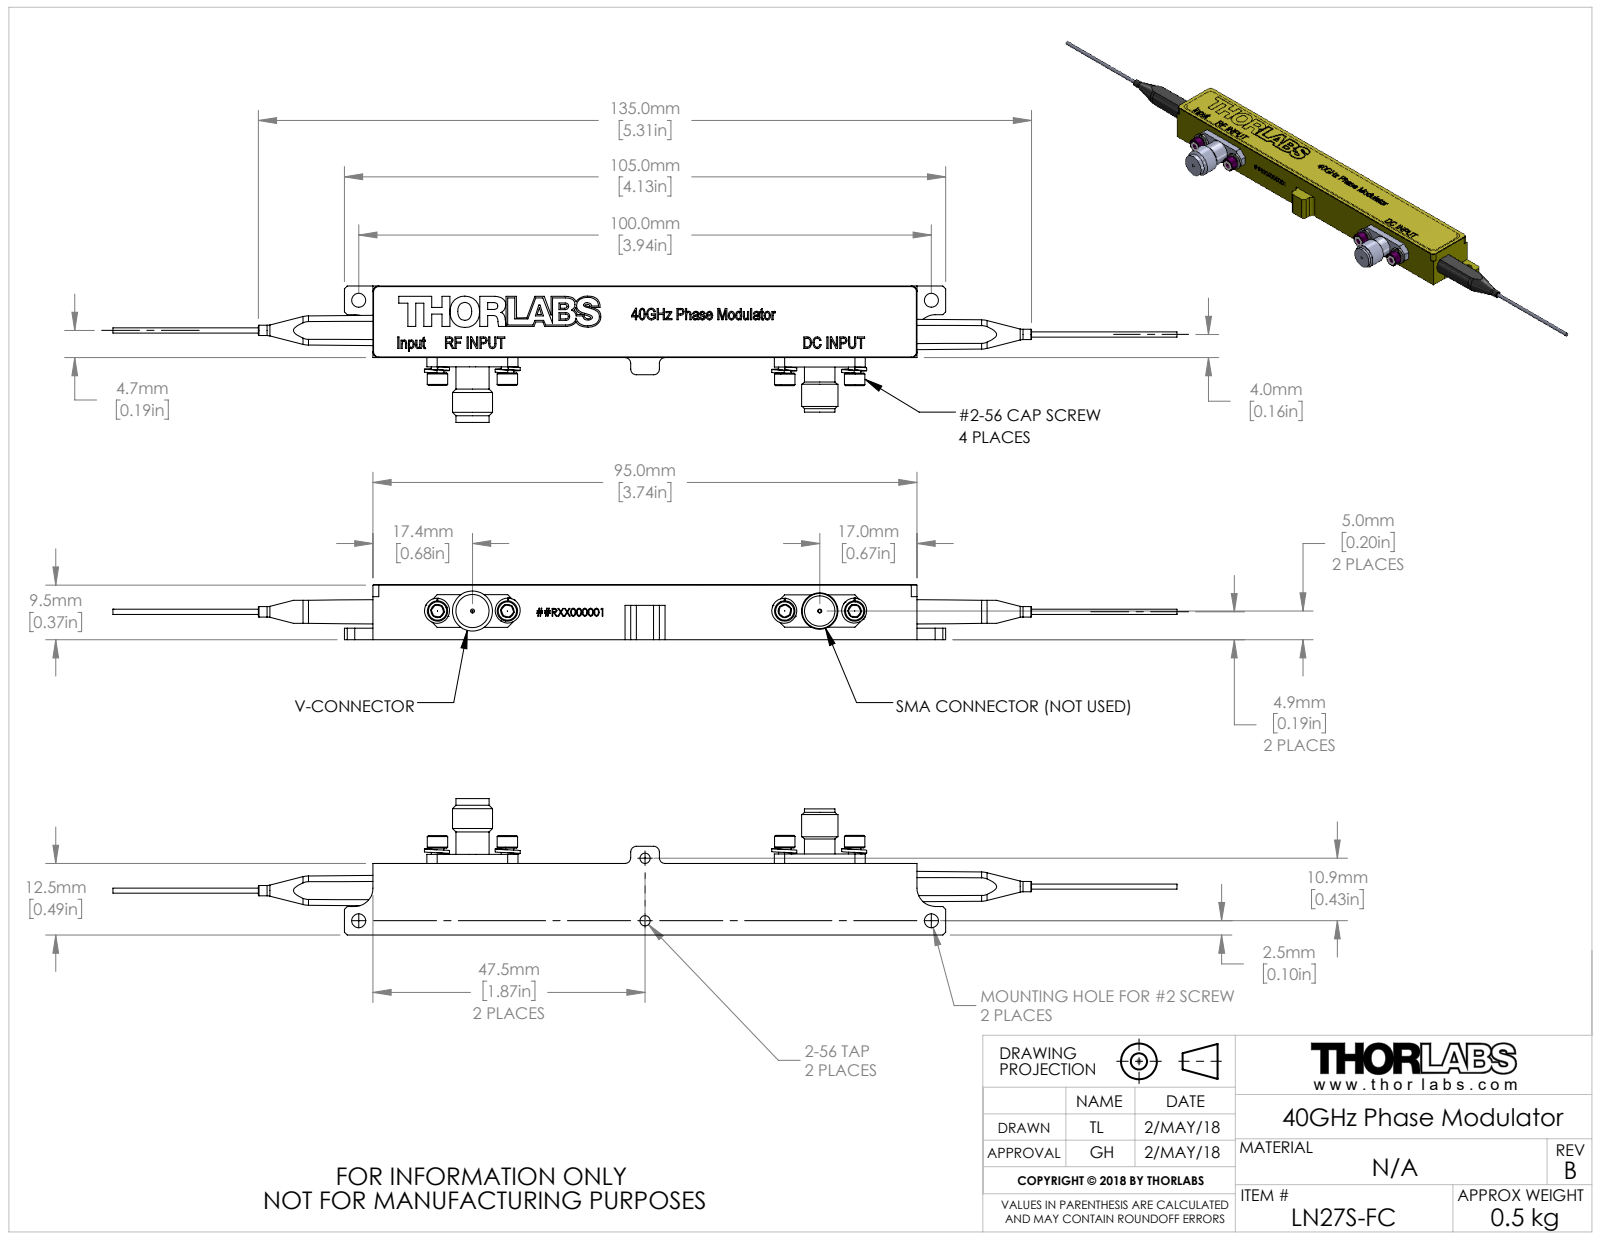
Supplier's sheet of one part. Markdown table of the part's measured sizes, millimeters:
| quantity | value |
| --- | --- |
| part name | 20857-E0W |
| STEP written by | SolidWorks 2016 (CONFIG_CONTROL_DESIGN) |
| units | millimeters |
| bodies | 0 solids, 583 faces (350 planar, 62 cylindrical, 171 other) |
| overall size | 185.8 × 23.81 × 9.63 |
| round holes (diameter × count) | 0.7 × 2, 1.78 × 2, 2.44 × 2 |
| round bosses / shafts (diameter × count) | 3.56 × 4, 2.18 × 4, 1.8 × 2, 0.9 × 2, 7 × 1, 6.35 × 1, 5.8 × 1, 5.31 × 1 |
| partial cylindrical surfaces (radius × count) | 1 × 8, 0.9 × 4, 3.18 × 2 |
| main face-to-face distances | 9.63, 12.5, 9.5, 9.58, 95, 1.65, 14.15, 7.58, 7.5, 14.1 |
| hole center spacings | 50, 51.17, 10.9, 60.64, 100 |
